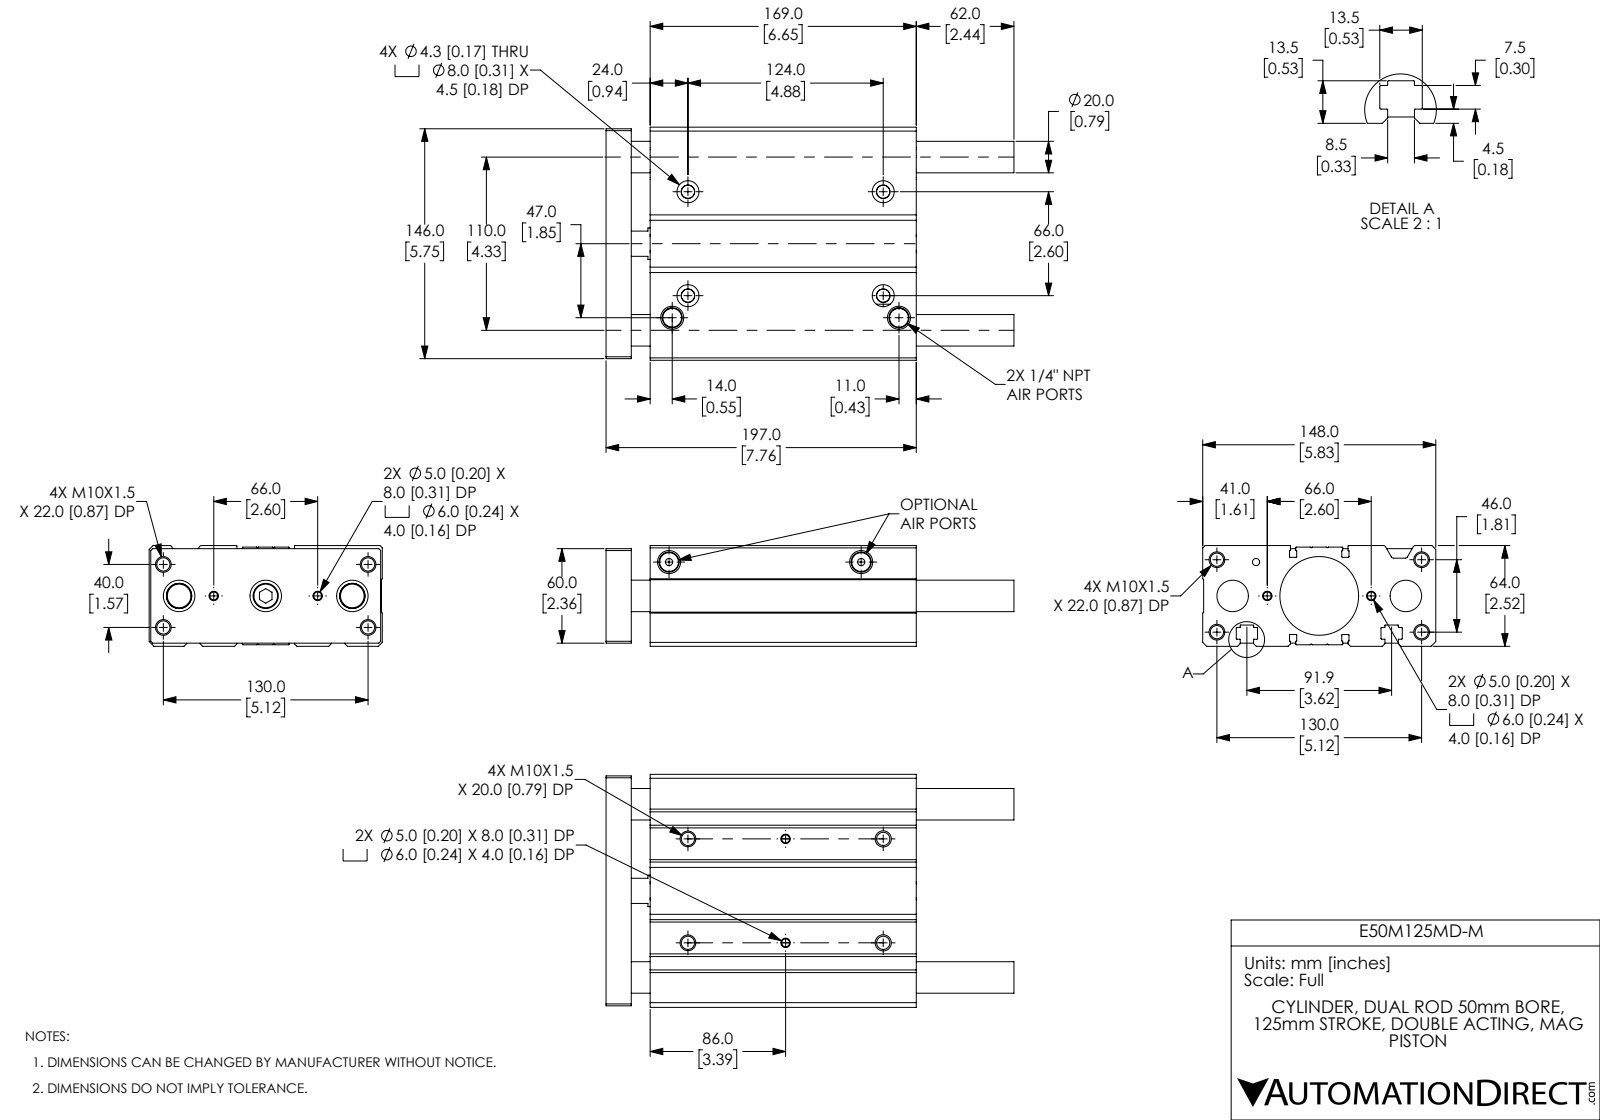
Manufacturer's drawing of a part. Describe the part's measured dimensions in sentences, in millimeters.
The part is named "E50M125MD-M; E50M125MD-M_ENDPLATE; E50M125MD-M_BODY". Its 3-D file was written by "SolidWorks 2019 (CONFIG_CONTROL_DESIGN)". It is 5 solids with 424 faces: 139 planar, 191 cylindrical and 94 other. Overall it measures 259 by 148 by 64 millimeters. Its volume is 1 437 000 cubic millimeters and its surface area 253 350 square millimeters. Round holes: 12 of diameter 8.38, 4 of diameter 5, 4 of diameter 6, 4 of diameter 8.6, 4 of diameter 14, 3 of diameter 4.57, 3 of diameter 10, 3 of diameter 20, 2 of diameter 16, 1 of diameter 20, 1 of diameter 50, 1 of diameter 50. Round bosses or shafts: 1 of diameter 16. Partial cylindrical surfaces (rounded edges, fillets, slot ends): 32 of radius 0.2, 28 of radius 0.4, 4 of radius 1.5, 2 of radius 0.3, 1 of radius 5. The main face-to-face distances are 1, 64, 62, 63, 12, 28, 16, 5.5, 148, 197. The hole center spacings are 3, 22.36, 25.08, 37.74, 39.41, 43, 62, 66.
